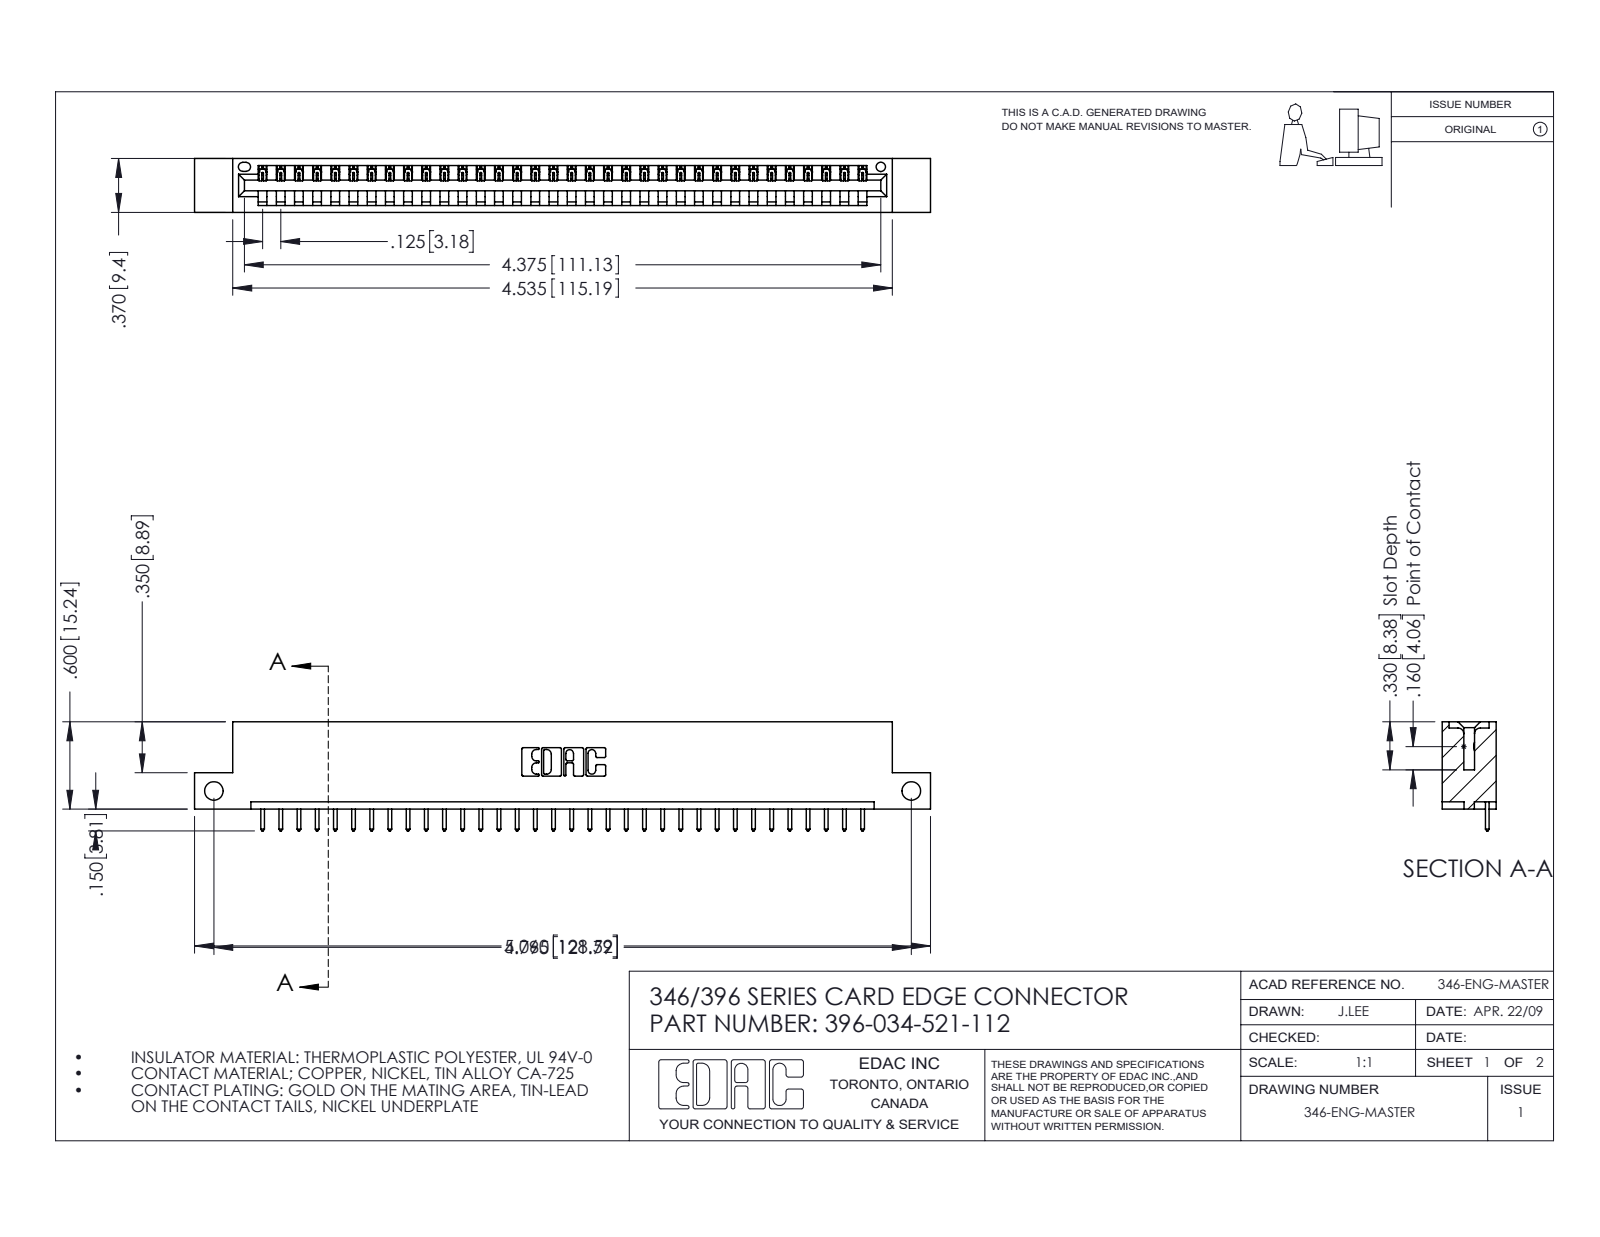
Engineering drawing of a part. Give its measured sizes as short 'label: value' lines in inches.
name: 396-034-521-112; 345-292-001_345-293-121; 346 Part_Flush Mounting Lugs - Side Mount
written by: SolidWorks 2016 (CONFIG_CONTROL_DESIGN)
unit: in
bodies: 35 solids, 2094 faces (1436 planar, 658 cylindrical, 0 other)
size: 5.06 × 0.75 × 0.37
volume: 0.736 in³; area: 22.41 in²
holes: 2× ⌀0.128, 1× ⌀0.064
rounds: 68× R0.006, 68× R0.01, 22× R0.01, 6× R0.007, 6× R0.031, 3× R0.026, 2× R0.031, 2× R0.04
face distances: 0.048, 0.322, 0.37, 0.25, 0.072, 0.298, 0.025, 0.148, 0.222, 0.1
hole spacings: 4.795
